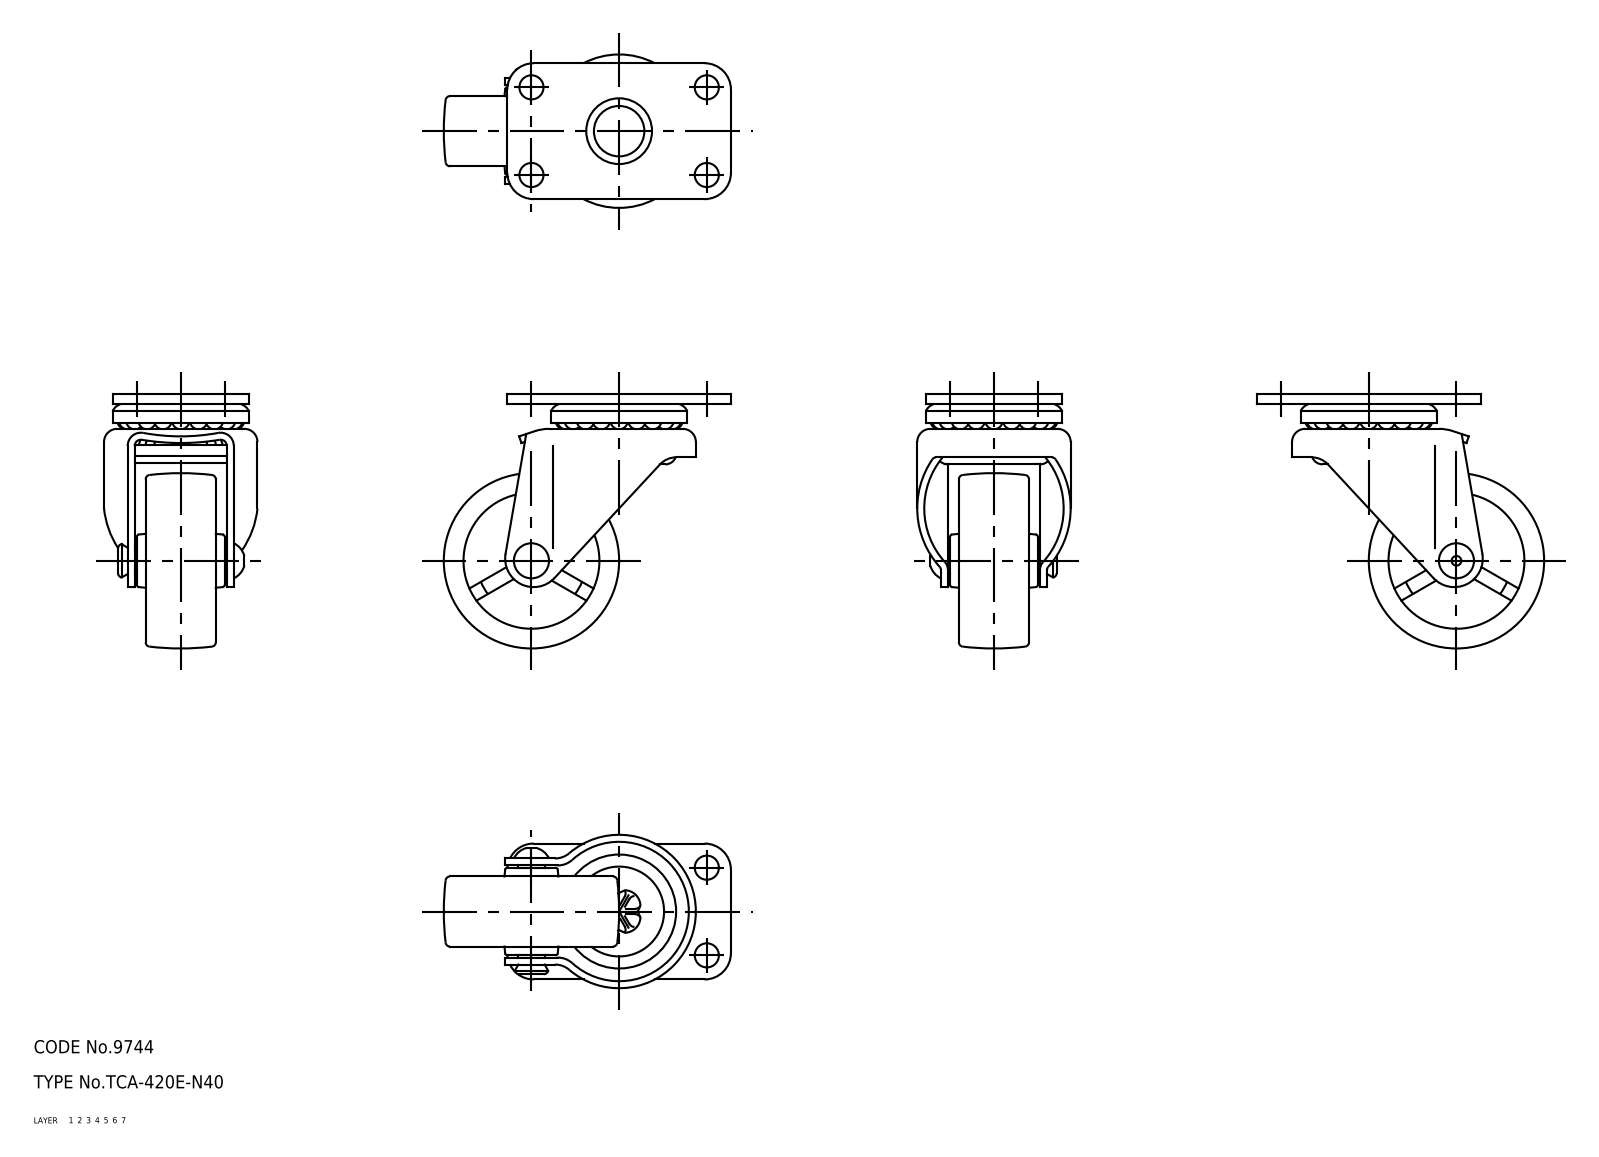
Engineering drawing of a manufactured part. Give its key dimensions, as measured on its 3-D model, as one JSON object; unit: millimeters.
{"part_name": "wheel; mounting plate; main shaft; axle (+1 more)", "step_written_by": "CADfix (AUTOMOTIVE_DESIGN)", "units": "millimeters", "bodies": {"solids": 5, "faces": 289, "planar": 0, "cylindrical": 0, "other": 289}, "overall_size": [65.5, 58, 35], "volume_mm3": 27910, "surface_area_mm2": 18832}
